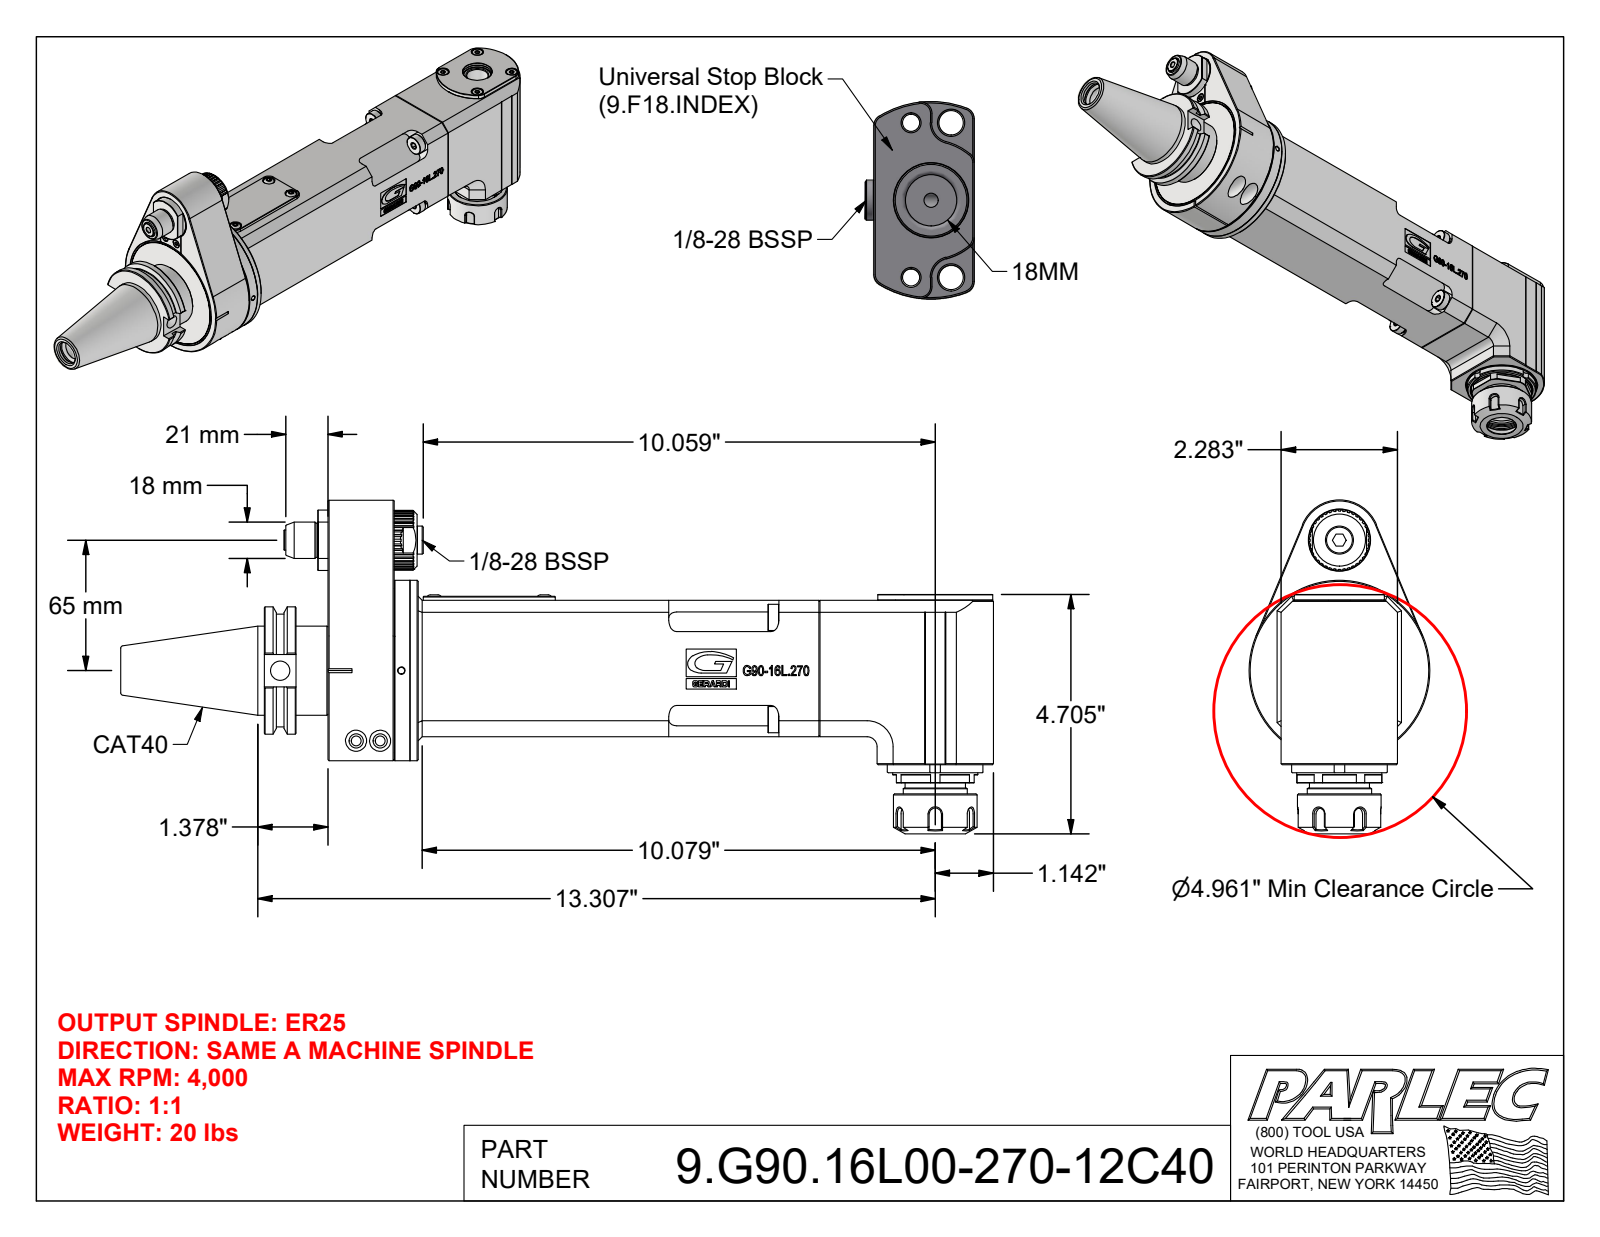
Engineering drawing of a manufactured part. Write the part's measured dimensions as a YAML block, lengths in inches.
part_name: "9.G90.16L00-270-12C40; G90-16L-270; 9_GA1_446_1 (Classic, Type 1, Cat40, 65mm)"
step_written_by: "Autodesk Inventor 2022 (AUTOMOTIVE_DESIGN)"
units: inches
bodies: {solids: 21, faces: 1476, planar: 732, cylindrical: 261, other: 483}
overall_size: [17.142, 6.555, 3.543]
volume: 69.47
surface_area: 388.9
round_holes:
  - {diameter: 0.197, count: 8}
  - {diameter: 0.13, count: 6}
  - {diameter: 0.335, count: 6}
  - {diameter: 0.315, count: 5}
  - {diameter: 0.165, count: 4}
  - {diameter: 0.157, count: 3}
  - {diameter: 0.236, count: 3}
  - {diameter: 0.709, count: 3}
  - {diameter: 0.276, count: 2}
  - {diameter: 0.413, count: 2}
  - {diameter: 0.551, count: 2}
  - {diameter: 1.201, count: 2}
round_bosses_or_shafts:
  - {diameter: 0.512, count: 4}
  - {diameter: 0.307, count: 4}
  - {diameter: 0.299, count: 4}
  - {diameter: 1.181, count: 2}
  - {diameter: 3.543, count: 1}
  - {diameter: 3.228, count: 1}
  - {diameter: 3.071, count: 1}
  - {diameter: 2.5, count: 1}
partial_cylinders:
  - {radius: 0.157, count: 16}
  - {radius: 0.118, count: 7}
  - {radius: 0.098, count: 5}
  - {radius: 0.197, count: 5}
  - {radius: 0.236, count: 4}
  - {radius: 0.085, count: 2}
  - {radius: 0.151, count: 2}
  - {radius: 0.079, count: 1}
face_to_face_distances: [2.283, 2.677, 1.299, 0.315, 0.118, 0.039, 0.197, 0.354, 0.984, 1.181]
hole_center_spacings: [0.678, 1.39, 1.476, 2.557, 0.551, 0.78, 0.945, 1.336]
